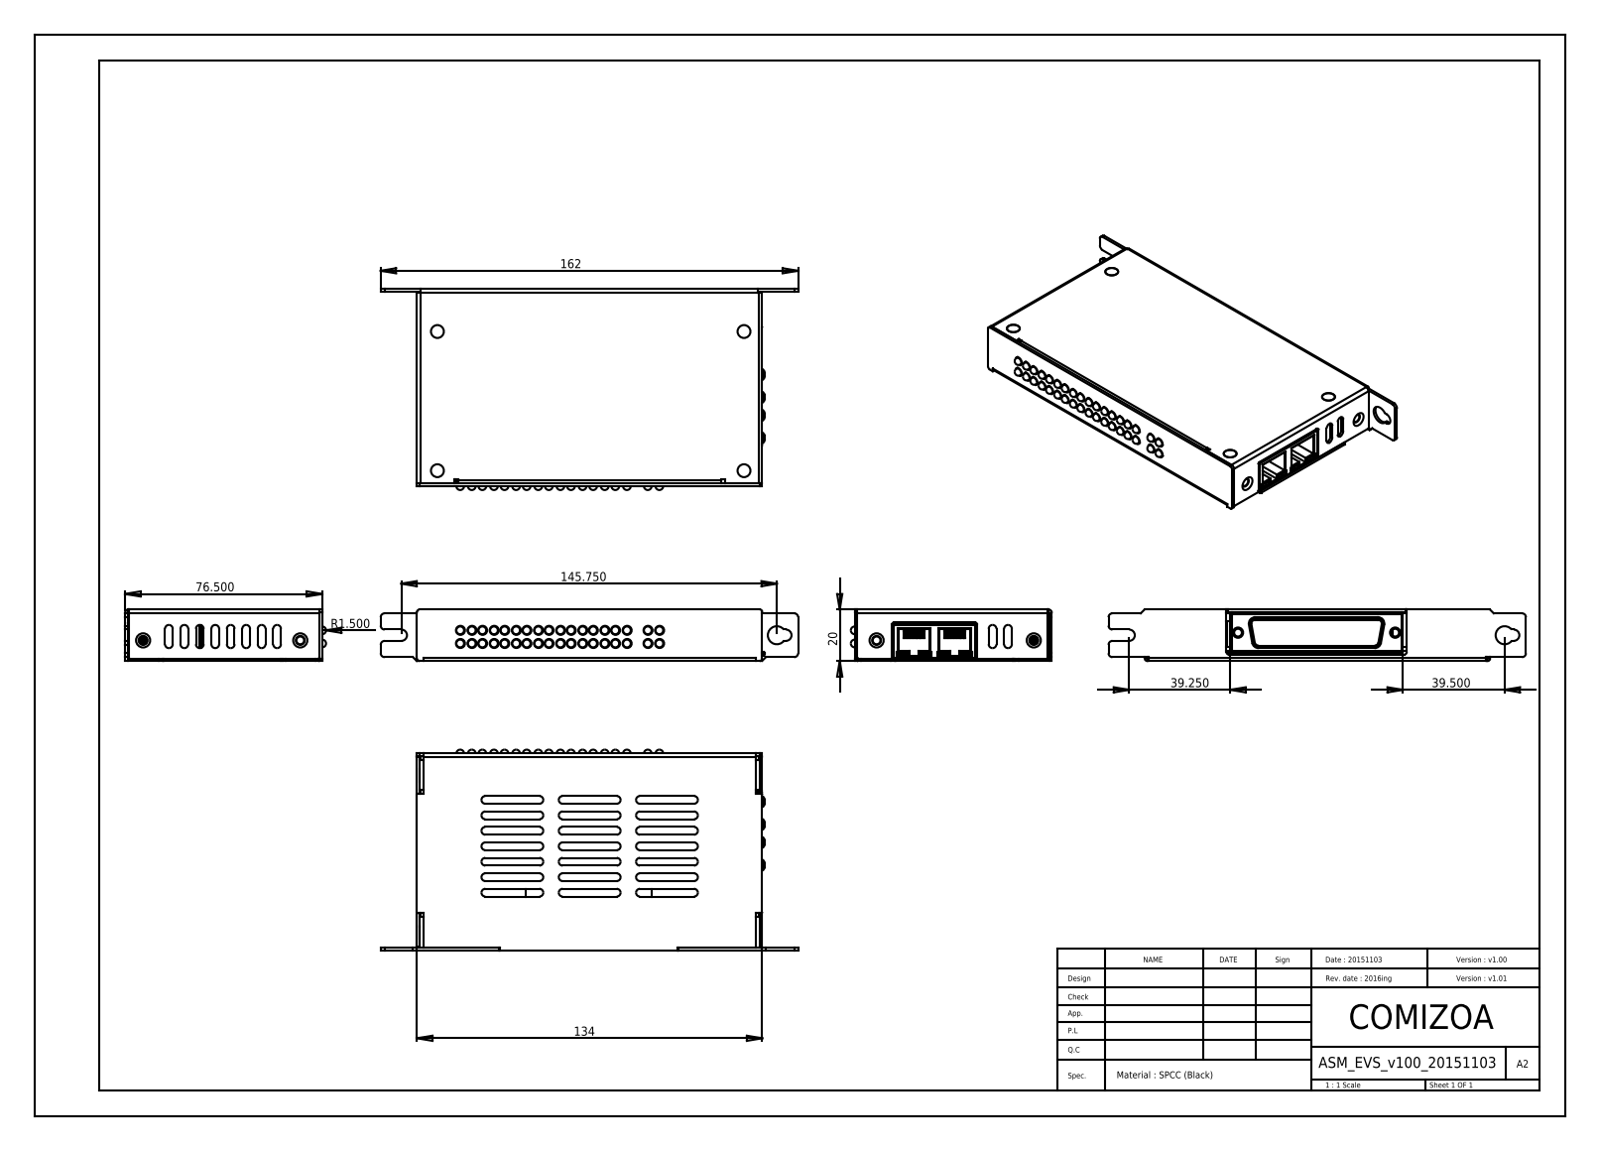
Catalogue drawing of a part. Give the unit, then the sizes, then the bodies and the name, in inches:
Units: inches
Overall size (bounding box): 6.378 × 3.071 × 0.787
Round holes (diameter × count): ⌀0.039 ×40, ⌀0.138 ×40, ⌀0.118 ×6, ⌀0.197 ×6
Round bosses / shafts (diameter × count): ⌀0.02 ×72, ⌀0.118 ×36
Partial cylindrical surfaces — rounded edges, fillets, slot ends (radius × count): R0.059 ×72, R0.02 ×43, R0.012 ×26, R0.079 ×8, R0.051 ×7, R0.039 ×6, R0.024 ×4, R0.031 ×2
Main face-to-face distances: 0.039, 0.748, 0.22, 0.181, 0.528, 0.787, 0.709, 0.567, 0.118, 0.591
Hole centre spacings: 0.339, 0.394, 0.201, 0.177, 0.268, 0.677, 0.706, 1.016
Volume: 3.941 in³ · Surface area: 133.3 in²
Bodies: 78 solids, 1734 faces (690 planar, 841 cylindrical, 203 other)
Part name (STEP PRODUCT): PRT_EVS32_FRONT_v100_20151103; IO_LED; Power_LED; RJ45_ASM (+8 more)
STEP written by: SolidWorks 2012 (CONFIG_CONTROL_DESIGN)
